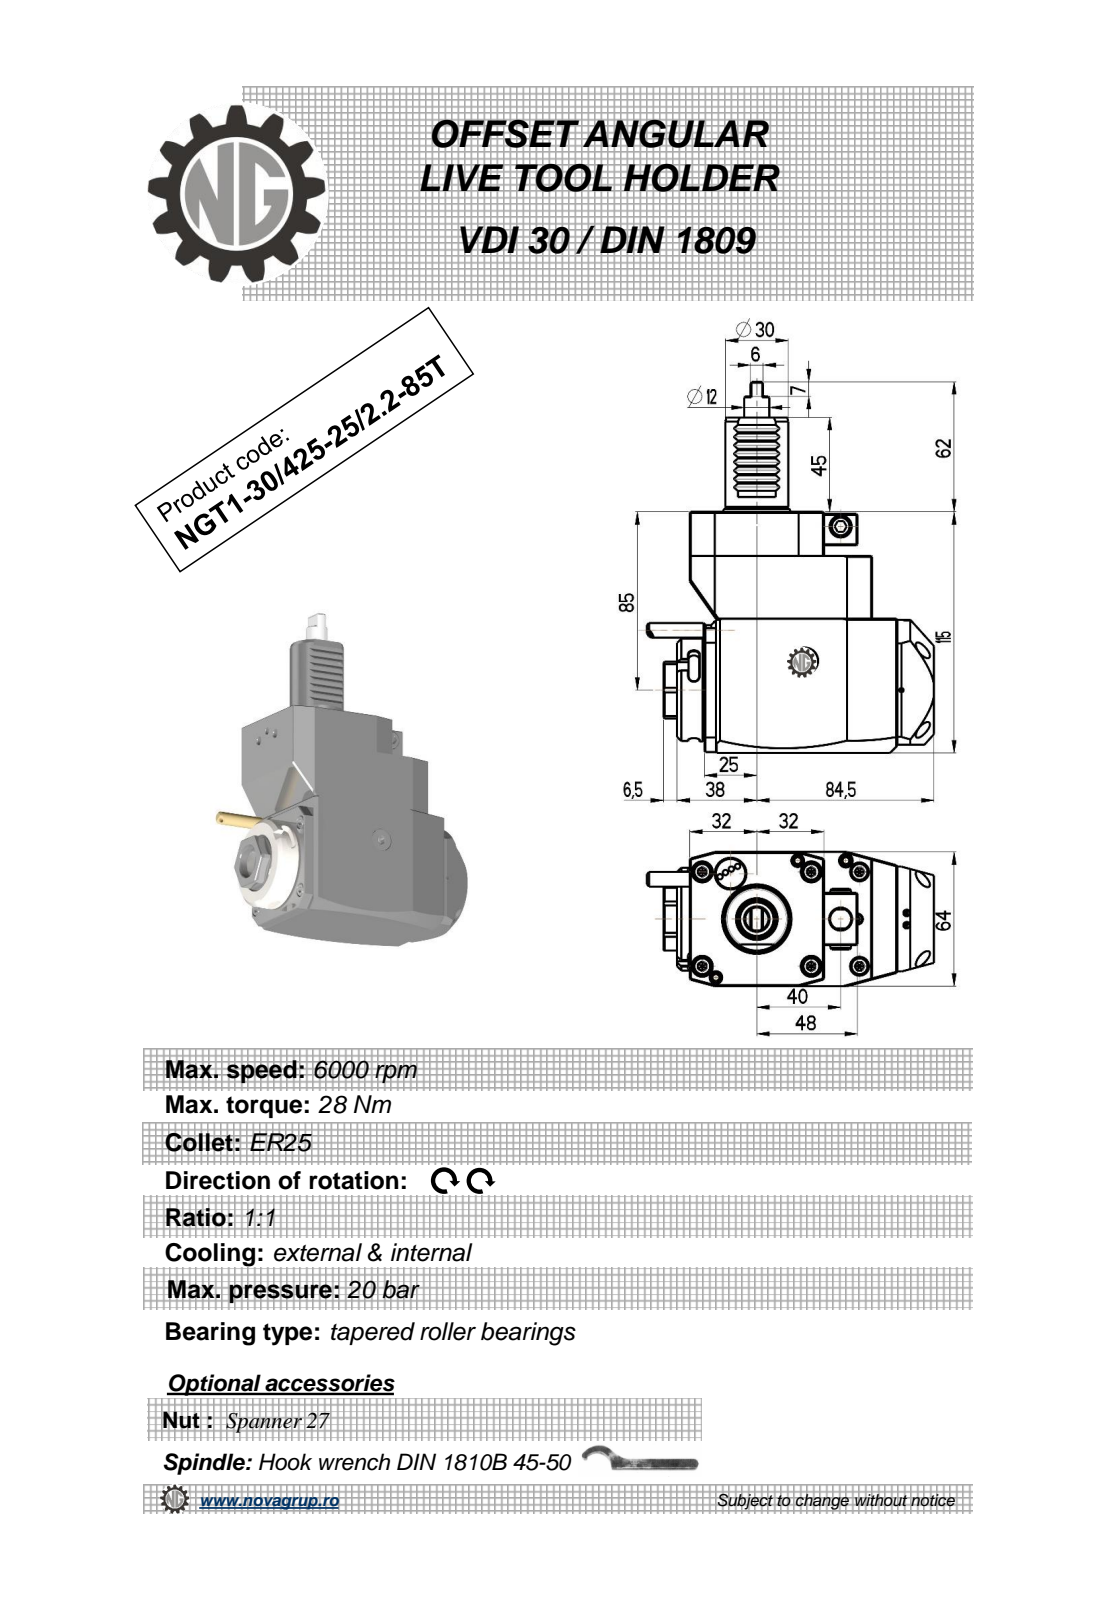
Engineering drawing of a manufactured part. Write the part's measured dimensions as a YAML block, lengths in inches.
part_name: "NGT1_30_425_25_1_2_85T"
step_written_by: "PRO/ENGINEER BY PARAMETRIC TECHNOLOGY CORPORATION, 2010280 (CONFIG_CONTROL_DESIGN)"
units: inches
bodies: {solids: 1, faces: 325, planar: 187, cylindrical: 68, other: 70}
overall_size: [6.969, 5.389, 2.52]
volume: 43.08
surface_area: 90.9
round_holes:
  - {diameter: 0.098, count: 1}
  - {diameter: 0.118, count: 1}
  - {diameter: 0.335, count: 1}
  - {diameter: 0.374, count: 1}
  - {diameter: 0.394, count: 1}
  - {diameter: 0.709, count: 1}
round_bosses_or_shafts:
  - {diameter: 0.353, count: 2}
  - {diameter: 1.929, count: 1}
  - {diameter: 1.654, count: 1}
  - {diameter: 1.181, count: 1}
  - {diameter: 0.472, count: 1}
  - {diameter: 0.394, count: 1}
  - {diameter: 0.276, count: 1}
  - {diameter: 0.197, count: 1}
partial_cylinders:
  - {radius: 0.012, count: 8}
  - {radius: 0.098, count: 6}
  - {radius: 0.031, count: 2}
  - {radius: 7.087, count: 2}
  - {radius: 0.177, count: 1}
  - {radius: 0.591, count: 1}
  - {radius: 0.846, count: 1}
  - {radius: 1.319, count: 1}
face_to_face_distances: [2.52, 4.528, 0.276, 3.15, 3.425, 0.236, 1.161, 3.701, 0.827, 4.587]
hole_center_spacings: [1.348, 2.032, 3.012]
